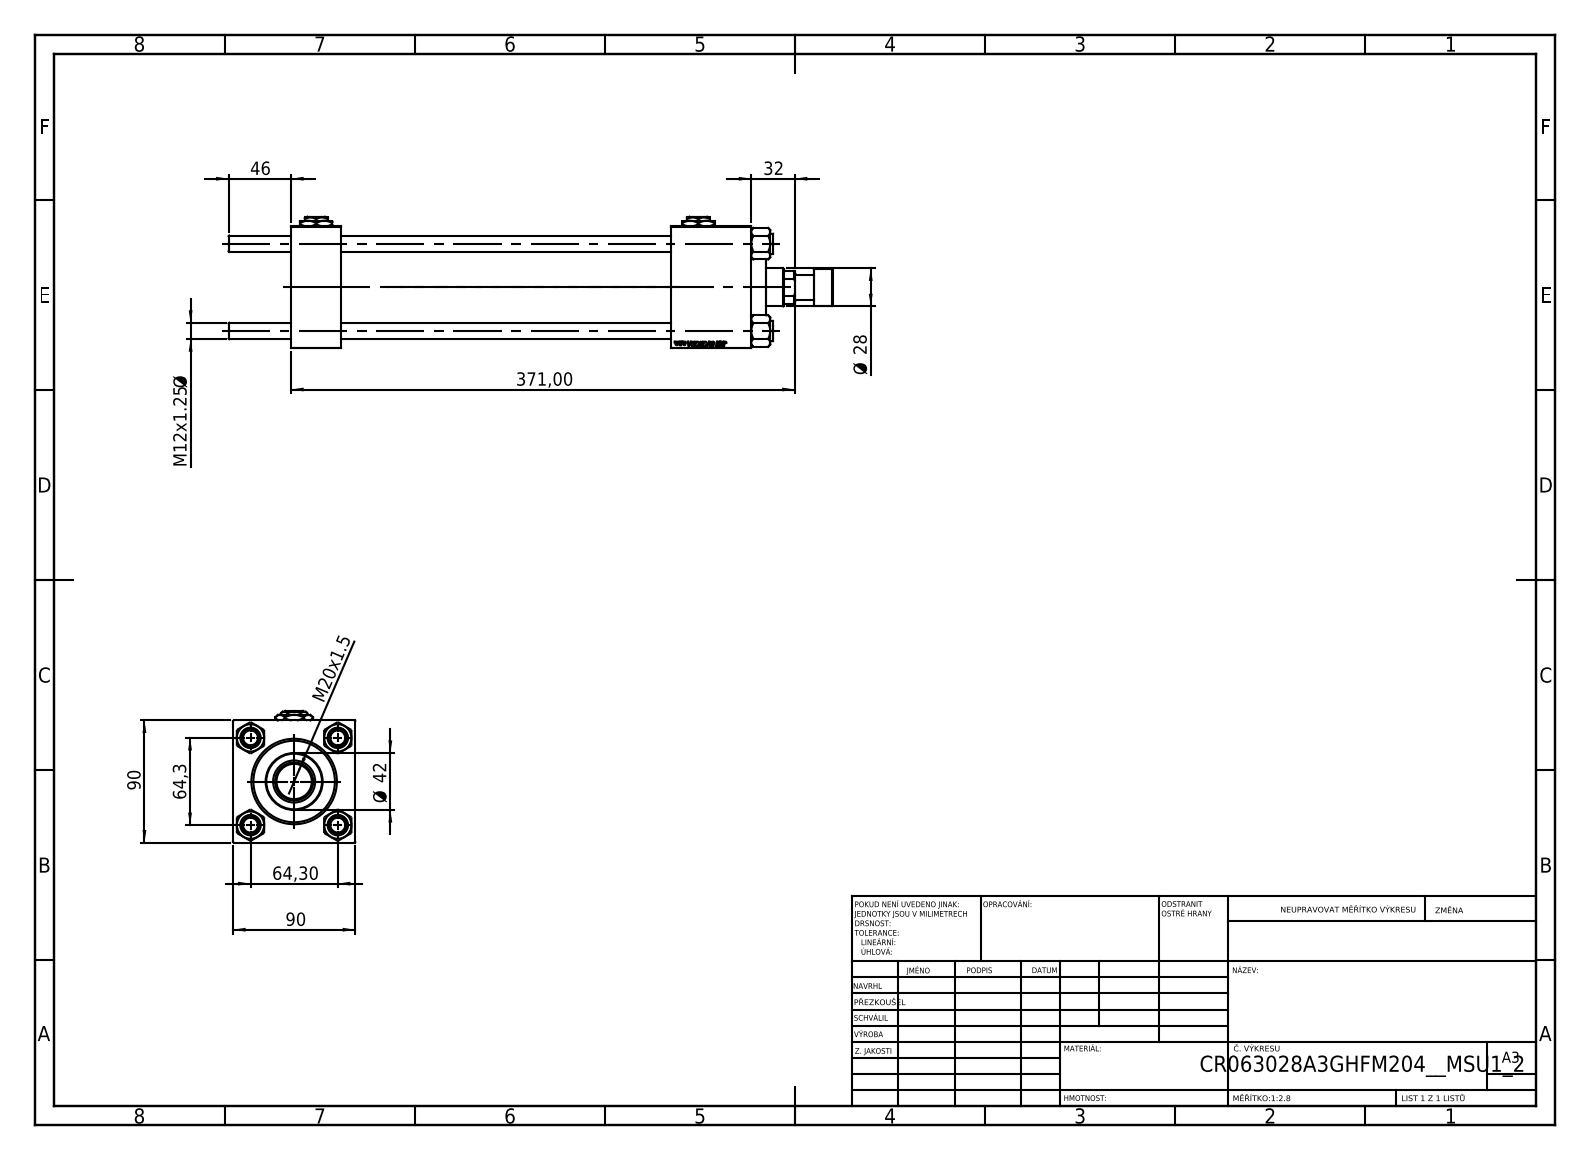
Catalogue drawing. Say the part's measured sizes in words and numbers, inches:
The part is named "Zatka_pro_OIL_PORT; NUT_M5; V215CR_VCP; V215_VC_A (+3 more)". Its 3-D file was written by "SolidWorks 2019 (CONFIG_CONTROL_DESIGN)". It is 14 solids with 1247 faces: 571 planar, 92 cylindrical and 584 other. Overall it measures 17.52 by 3.819 by 3.543 inches. Its volume is 79.15 cubic inches and its surface area 501.5 square inches. Round holes: 4 of diameter 0.472, 2 of diameter 0.276, 2 of diameter 0.825, 2 of diameter 1.181, 1 of diameter 0.728, 1 of diameter 1.102, 1 of diameter 1.22, 1 of diameter 1.969, 1 of diameter 2.362, 1 of diameter 2.48. Round bosses or shafts: 4 of diameter 0.591, 1 of diameter 2.717, 1 of diameter 1.654, 1 of diameter 1.063, 1 of diameter 0.709. The main face-to-face distances are 3.543, 1.457, 13.346, 11.89, 2.323, 11.024, 9.567, 12.217, 10.76, 1.193. The hole center spacings are 1.79, 2.531, 3.58, 11.083.
